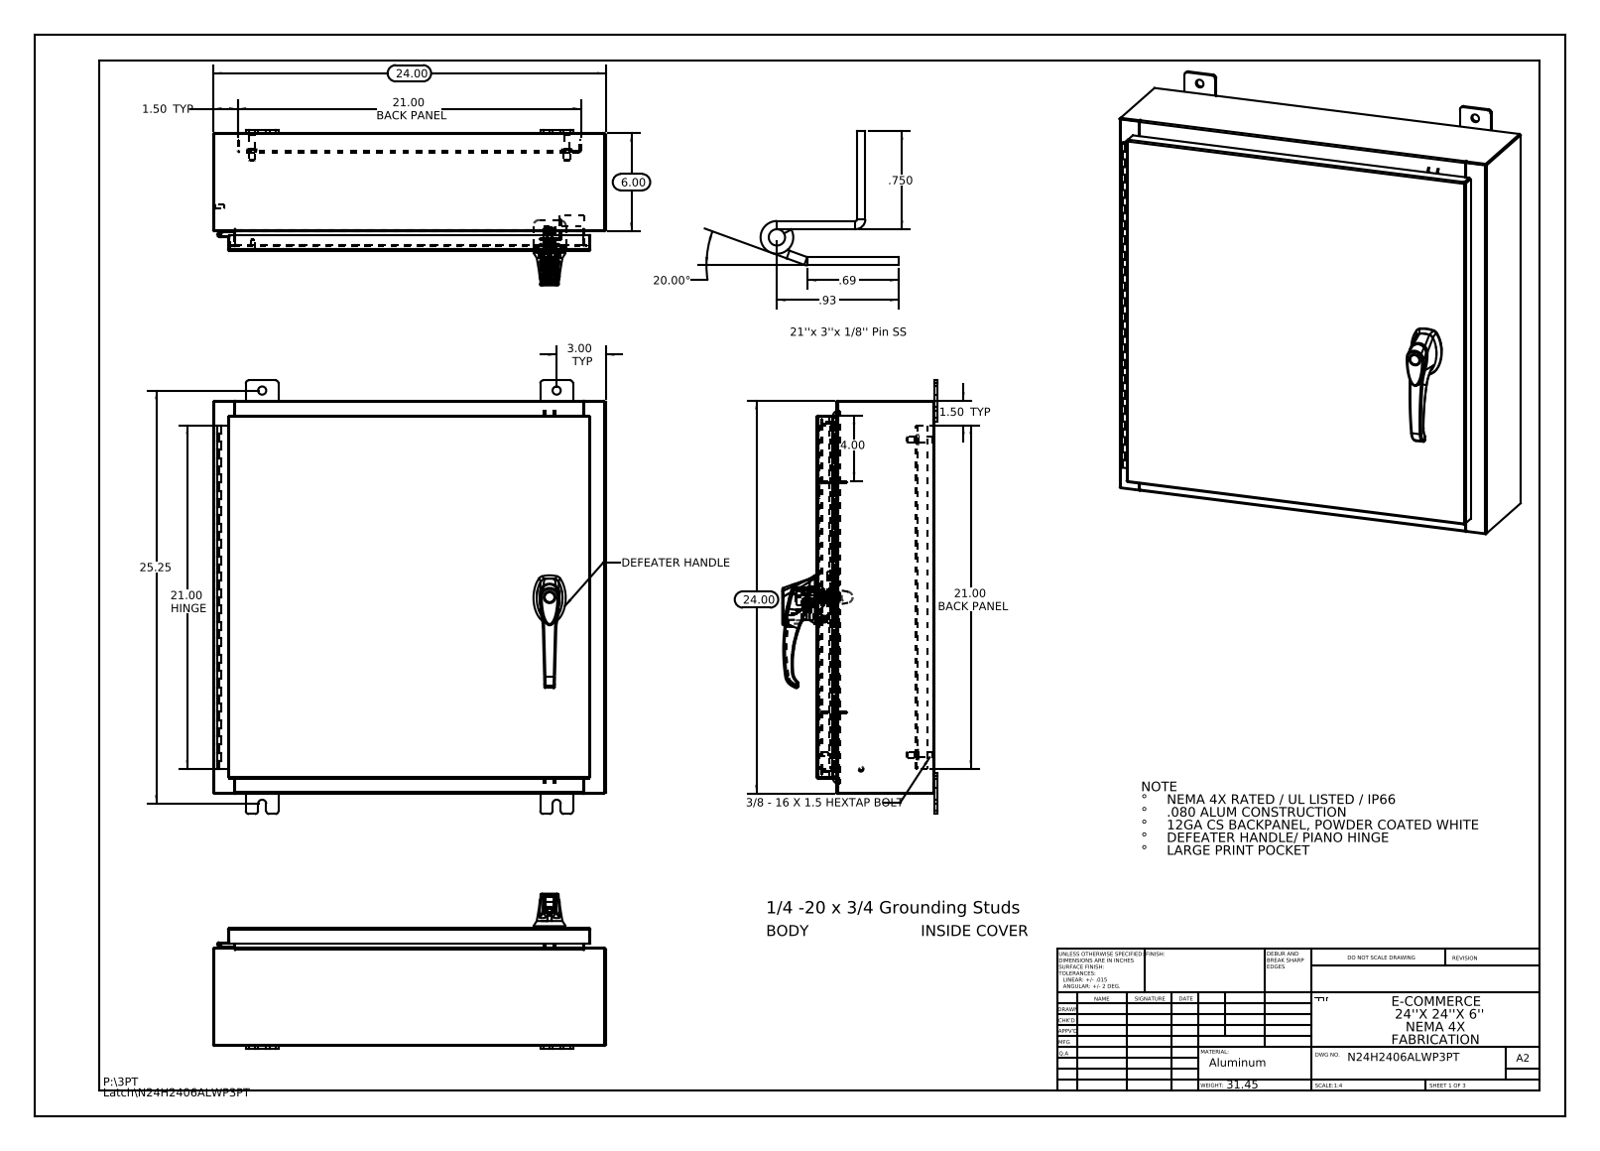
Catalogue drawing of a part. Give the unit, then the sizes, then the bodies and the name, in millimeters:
Units: millimetres
Overall size (bounding box): 673.1 × 609.6 × 241.2
Round holes (diameter × count): ⌀12.7 ×8, ⌀6.4 ×4, ⌀3.5 ×3, ⌀4.1 ×3, ⌀2 ×2, ⌀5.2 ×2, ⌀8 ×2, ⌀11.1 ×2, ⌀3.2 ×1, ⌀3.2 ×1, ⌀5 ×1, ⌀7 ×1
Round bosses / shafts (diameter × count): ⌀15.9 ×4, ⌀9.5 ×4, ⌀8.4 ×4, ⌀4 ×4, ⌀3.6 ×4, ⌀8 ×3, ⌀6 ×3, ⌀30 ×1
Partial cylindrical surfaces — rounded edges, fillets, slot ends (radius × count): R3 ×37, R0.2 ×33, R4.8 ×24, R0.3 ×22, R2.2 ×18, R1 ×15, R0.7 ×12, R0.2 ×6
Main face-to-face distances: 1.9, 181, 607.7, 179.1, 182.9, 2.6, 25.4, 27.3, 153.7, 155.6
Hole centre spacings: 195.1, 7.5, 15.9, 21.4, 31.8, 33.4, 39.6, 47.2
Volume: 3 428 000 mm³ · Surface area: 3 315 000 mm²
Bodies: 37 solids, 2498 faces (883 planar, 917 cylindrical, 698 other)
Part name (STEP PRODUCT): N24H2406ALWP3PT Mounting Feet; N24H2406ALWP3PT 263033_Industrilas; N24H2406ALWP3PT Cover; N24H2406ALWP3PT Bottom (+8 more)
STEP written by: SolidWorks 2013 (CONFIG_CONTROL_DESIGN)
